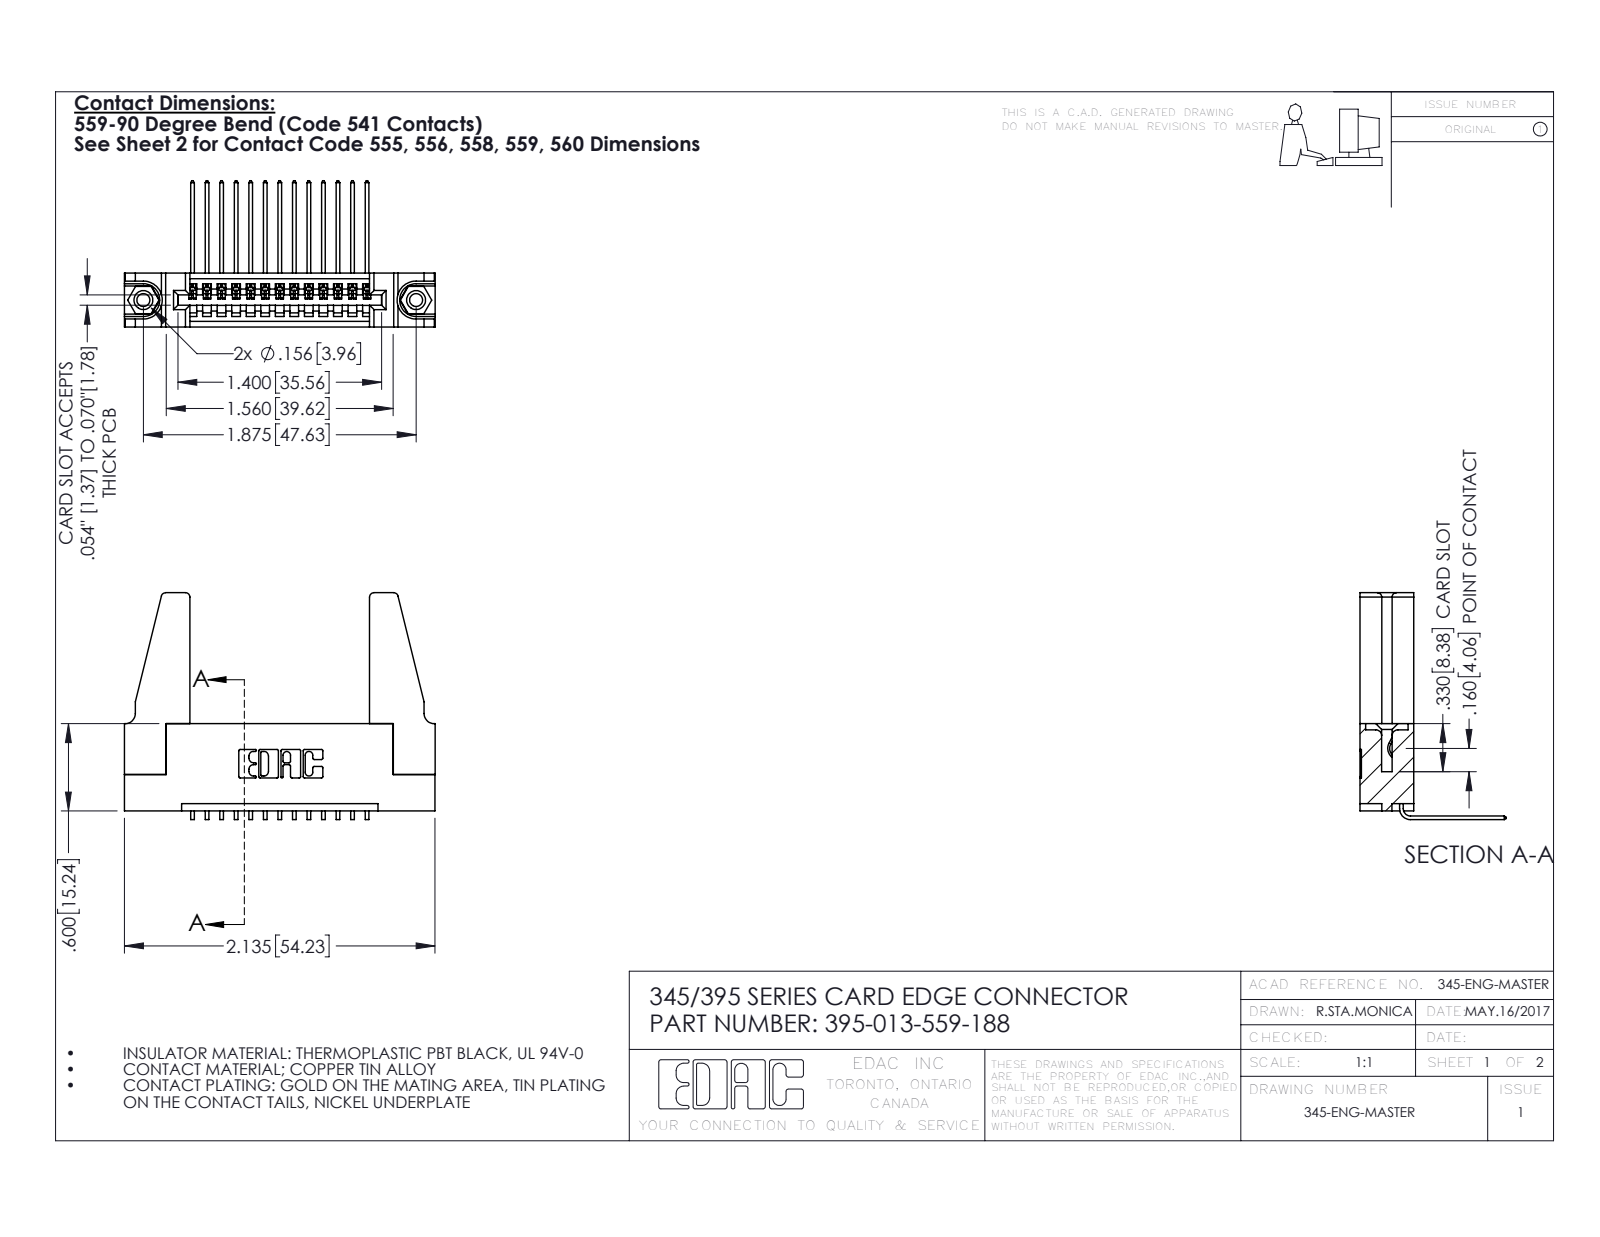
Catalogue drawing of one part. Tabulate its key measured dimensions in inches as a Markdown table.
| quantity | value |
| --- | --- |
| part name | 345 Part_Flush Mounting Lugs - 0.156 Dia-TH; 345-292-001_558 559 Tail - 1; 345-250-001_345-250-001-102; 395-013-559-188 (+1 more) |
| STEP written by | SolidWorks 2016 (CONFIG_CONTROL_DESIGN) |
| units | inches |
| bodies | 18 solids, 1030 faces (698 planar, 316 cylindrical, 16 other) |
| overall size | 2.136 × 1.559 × 1.005 |
| volume | 0.501 in³ |
| surface area | 14.85 in² |
| round holes (diameter × count) | 0.089 × 2, 0.125 × 2, 0.156 × 2, 0.064 × 1 |
| round bosses / shafts (diameter × count) | 0.155 × 2 |
| partial cylindrical surfaces (radius × count) | 0.006 × 26, 0.01 × 22, 0.03 × 8, 0.007 × 6, 0.031 × 6, 0.026 × 3, 0.031 × 2, 0.04 × 2 |
| main face-to-face distances | 0.37, 0.072, 0.298, 0.2, 0.098, 0.272, 0.025, 0.225, 0.148, 0.15 |
| hole center spacings | 0.27, 1.643, 1.875 |
